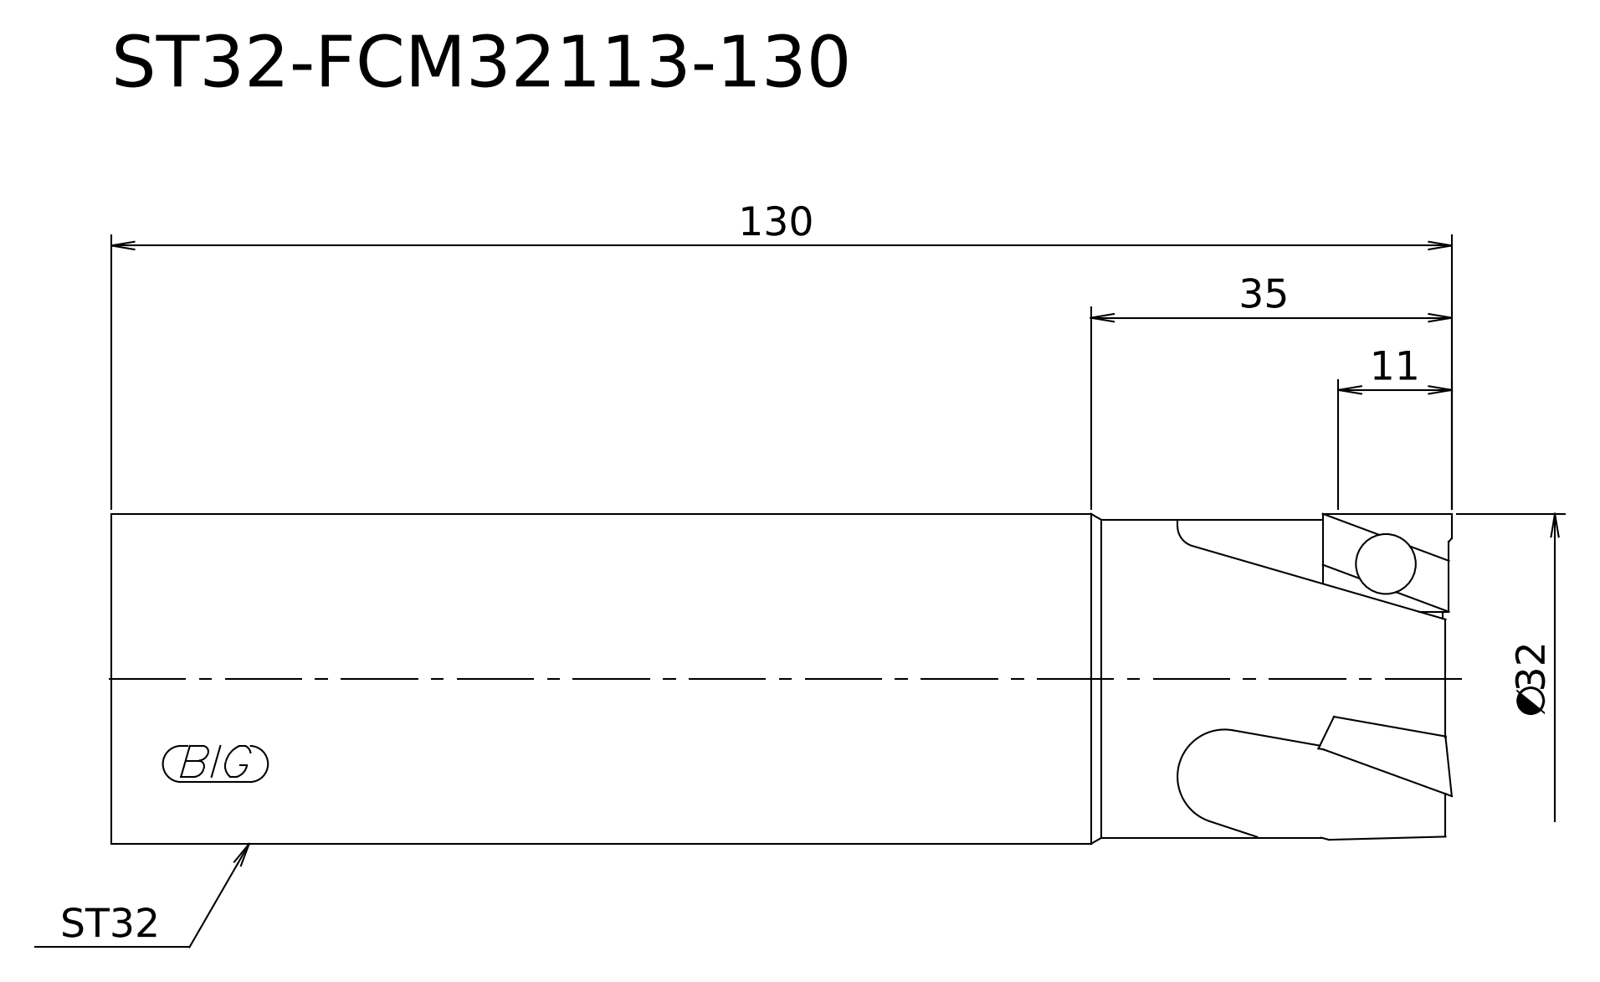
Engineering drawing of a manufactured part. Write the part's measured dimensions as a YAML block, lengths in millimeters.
step_written_by: "Kubotek KeyCreator V8.5.1 (14335) (CONFIG_CONTROL_DESIGN)"
units: millimeters
bodies: {solids: 1, faces: 7, planar: 3, cylindrical: 3, other: 1}
overall_size: [130, 32, 32]
volume: 103252
surface_area: 14670
round_bosses_or_shafts:
  - {diameter: 32, count: 1}
  - {diameter: 30.8, count: 1}
face_to_face_distances: [130, 12.51, 117.49]
